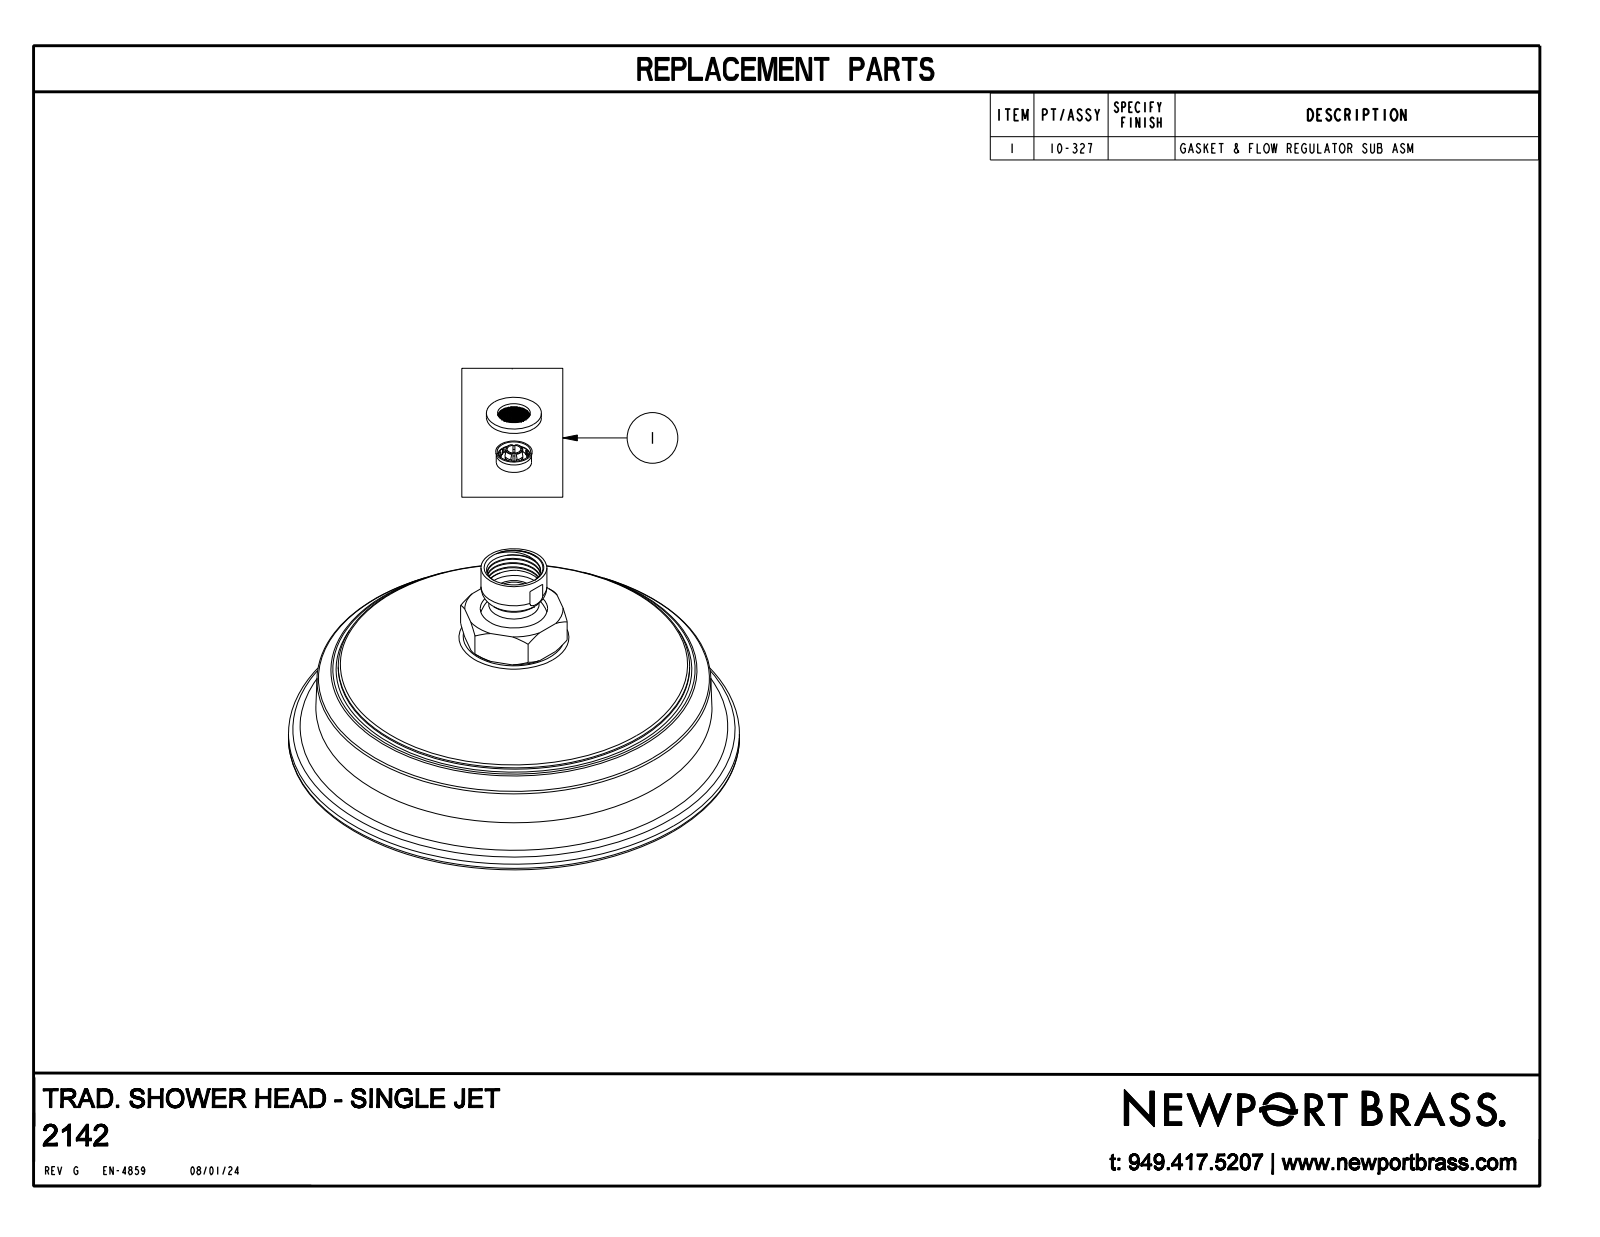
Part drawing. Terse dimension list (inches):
name: 1-200_1; 1-200_2; 1-200_ASM; 80152 (+5 more)
written by: CREO PARAMETRIC BY PTC INC, 2018400 (AUTOMOTIVE_DESIGN)
unit: in
bodies: 97 solids, 1726 faces (424 planar, 774 cylindrical, 528 other)
size: 6.2 × 6.2 × 3.306
volume: 9.504 in³; area: 216.1 in²
holes: 90× ⌀0.05, 90× ⌀0.125, 1× ⌀0.22, 1× ⌀0.453, 1× ⌀0.488, 1× ⌀0.526, 1× ⌀0.604, 1× ⌀0.917, 1× ⌀1.01, 1× ⌀1.189, 1× ⌀1.27, 1× ⌀4.9
bosses: 90× ⌀0.198, 1× ⌀6.2, 1× ⌀5.22, 1× ⌀5.1, 1× ⌀4.83, 1× ⌀1.42, 1× ⌀1.389, 1× ⌀1.25
face distances: 0.1, 0.065, 0.155, 0.03, 2.452, 2.352, 0.035, 0.22, 0.165, 2.517
hole spacings: 1.84, 1.41, 3.648, 0.48, 0.49, 1.41, 2.592, 3.187
